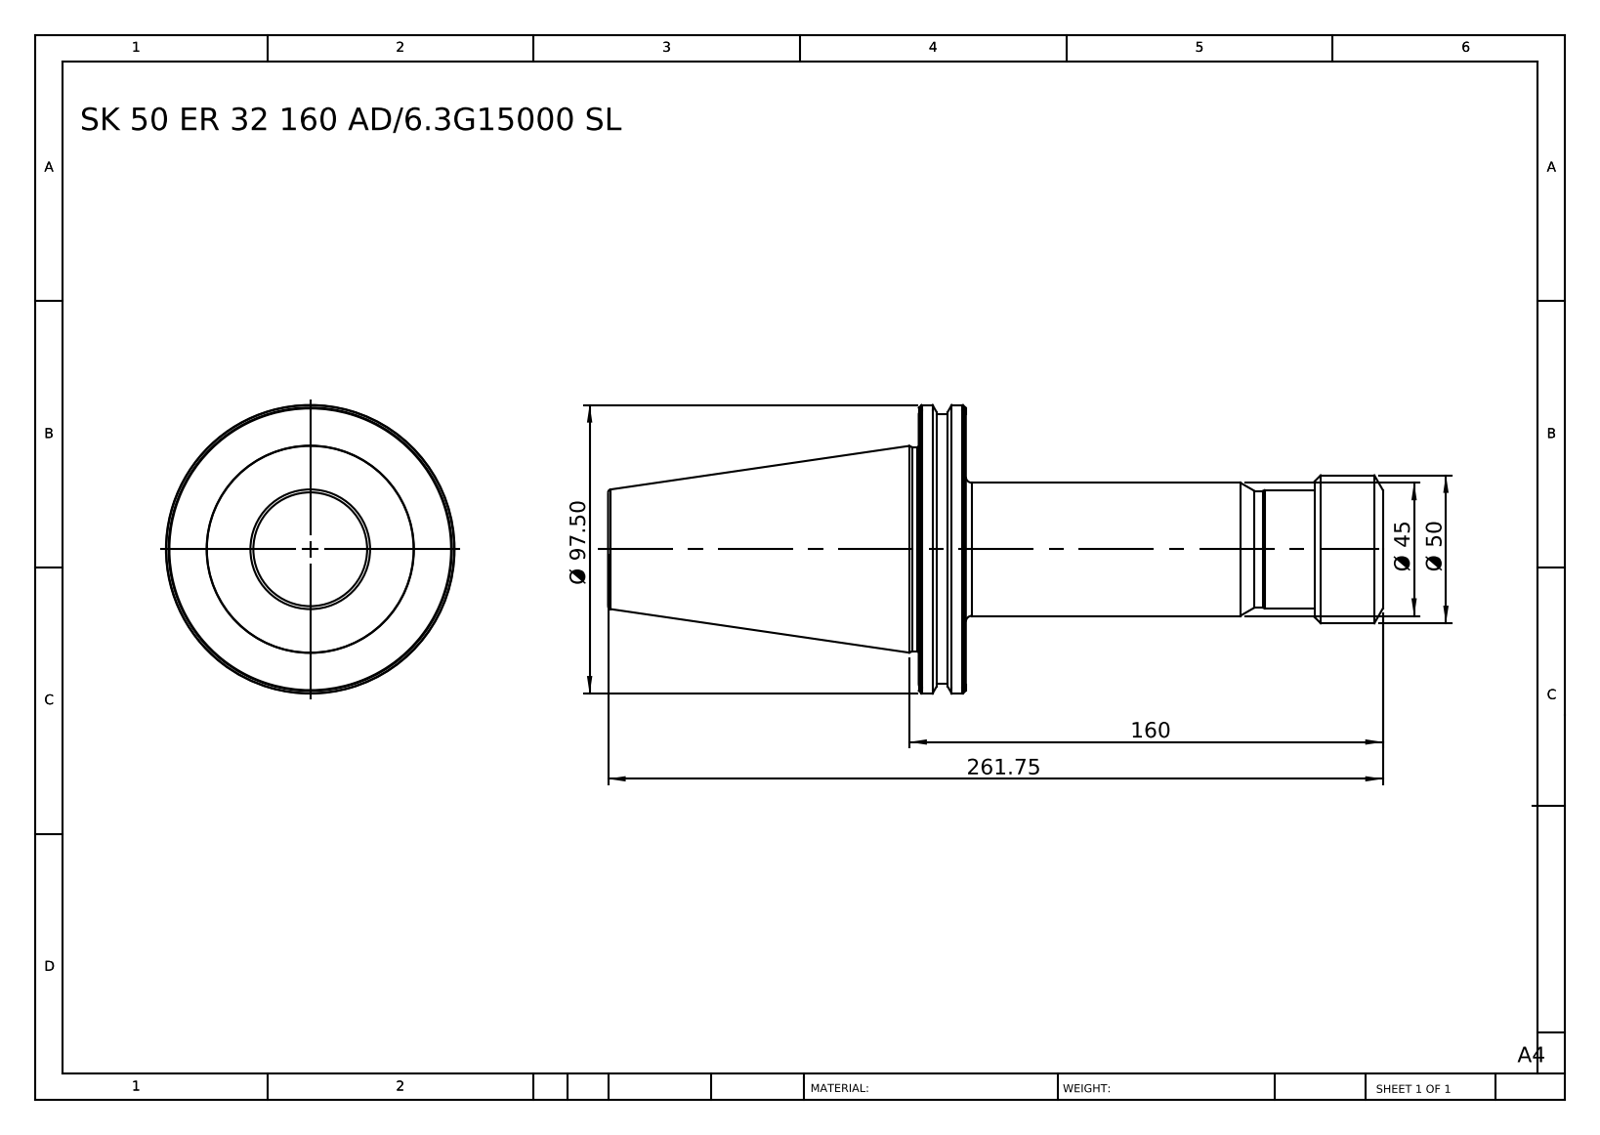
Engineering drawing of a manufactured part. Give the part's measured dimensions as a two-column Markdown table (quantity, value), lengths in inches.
| quantity | value |
| --- | --- |
| part name | SK 50 ER 32 160 AD-6.3G15000 SL |
| STEP written by | SolidWorks 2014 (CONFIG_CONTROL_DESIGN) |
| units | inches |
| bodies | 1 solid, 77 faces (7 planar, 16 cylindrical, 54 other) |
| overall size | 10.305 × 3.839 × 3.839 |
| volume | 36.43 in³ |
| surface area | 88.41 in² |
| round bosses / shafts (diameter × count) | 3.839 × 1, 3.583 × 1, 2.717 × 1, 1.969 × 1, 1.772 × 1, 1.571 × 1, 1.555 × 1 |
| main face-to-face distances | 0.626, 5.547, 6.173, 10.305, 4.758, 4.132, 0.906, 4.642, 5.268, 9.4 |
